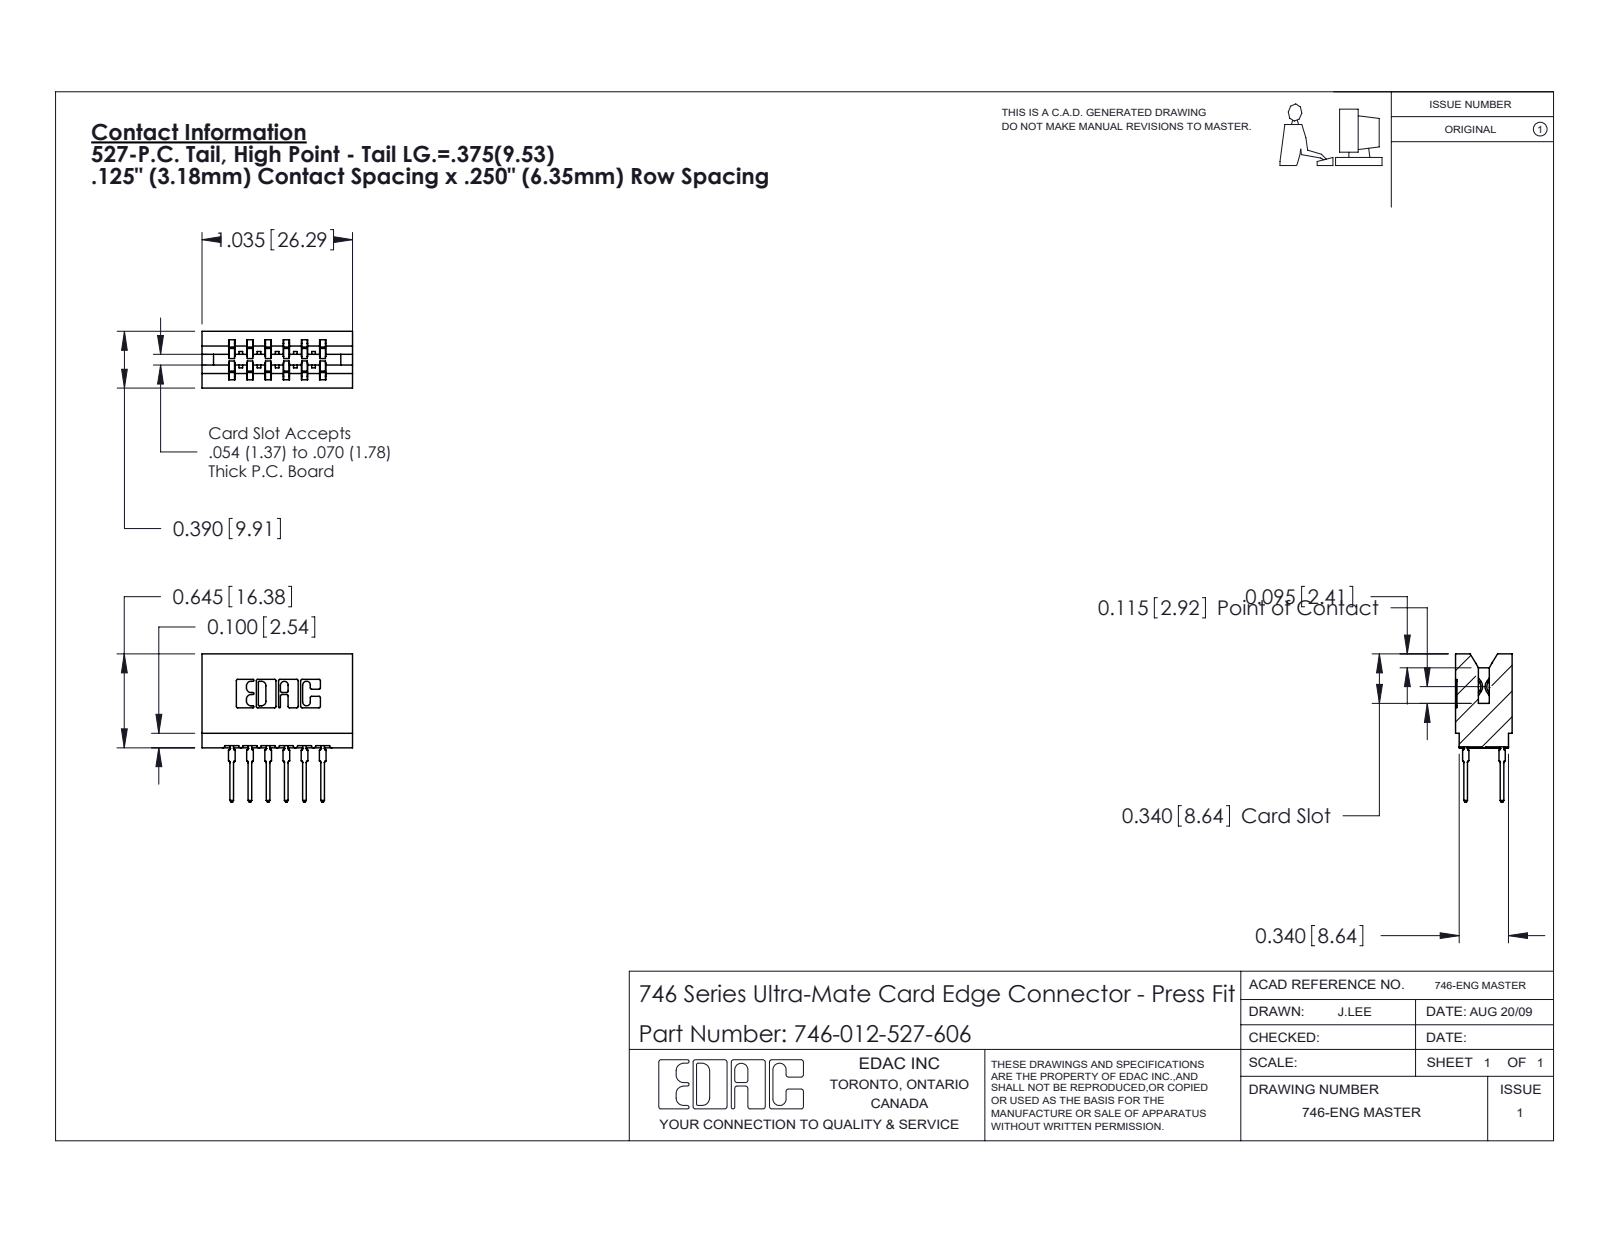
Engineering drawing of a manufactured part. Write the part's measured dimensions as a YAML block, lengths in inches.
part_name: "746-292-001_527; 746-012-527-606; 746 Part_.340 Slot Depth - 06"
step_written_by: "SolidWorks 2020 (CONFIG_CONTROL_DESIGN)"
units: inches
bodies: {solids: 13, faces: 1172, planar: 608, cylindrical: 252, other: 312}
overall_size: [1.035, 1.019, 0.39]
volume: 0.197
surface_area: 6.477
partial_cylinders:
  - {radius: 0.021, count: 24}
  - {radius: 0.01, count: 22}
  - {radius: 0.005, count: 8}
  - {radius: 0.011, count: 8}
  - {radius: 0.015, count: 7}
  - {radius: 0.007, count: 6}
  - {radius: 0.031, count: 6}
  - {radius: 0.026, count: 3}
face_to_face_distances: [0.25, 0.042, 0.125, 0.057, 0.333, 0.125, 0.375, 0.5, 0.39, 0.292]
